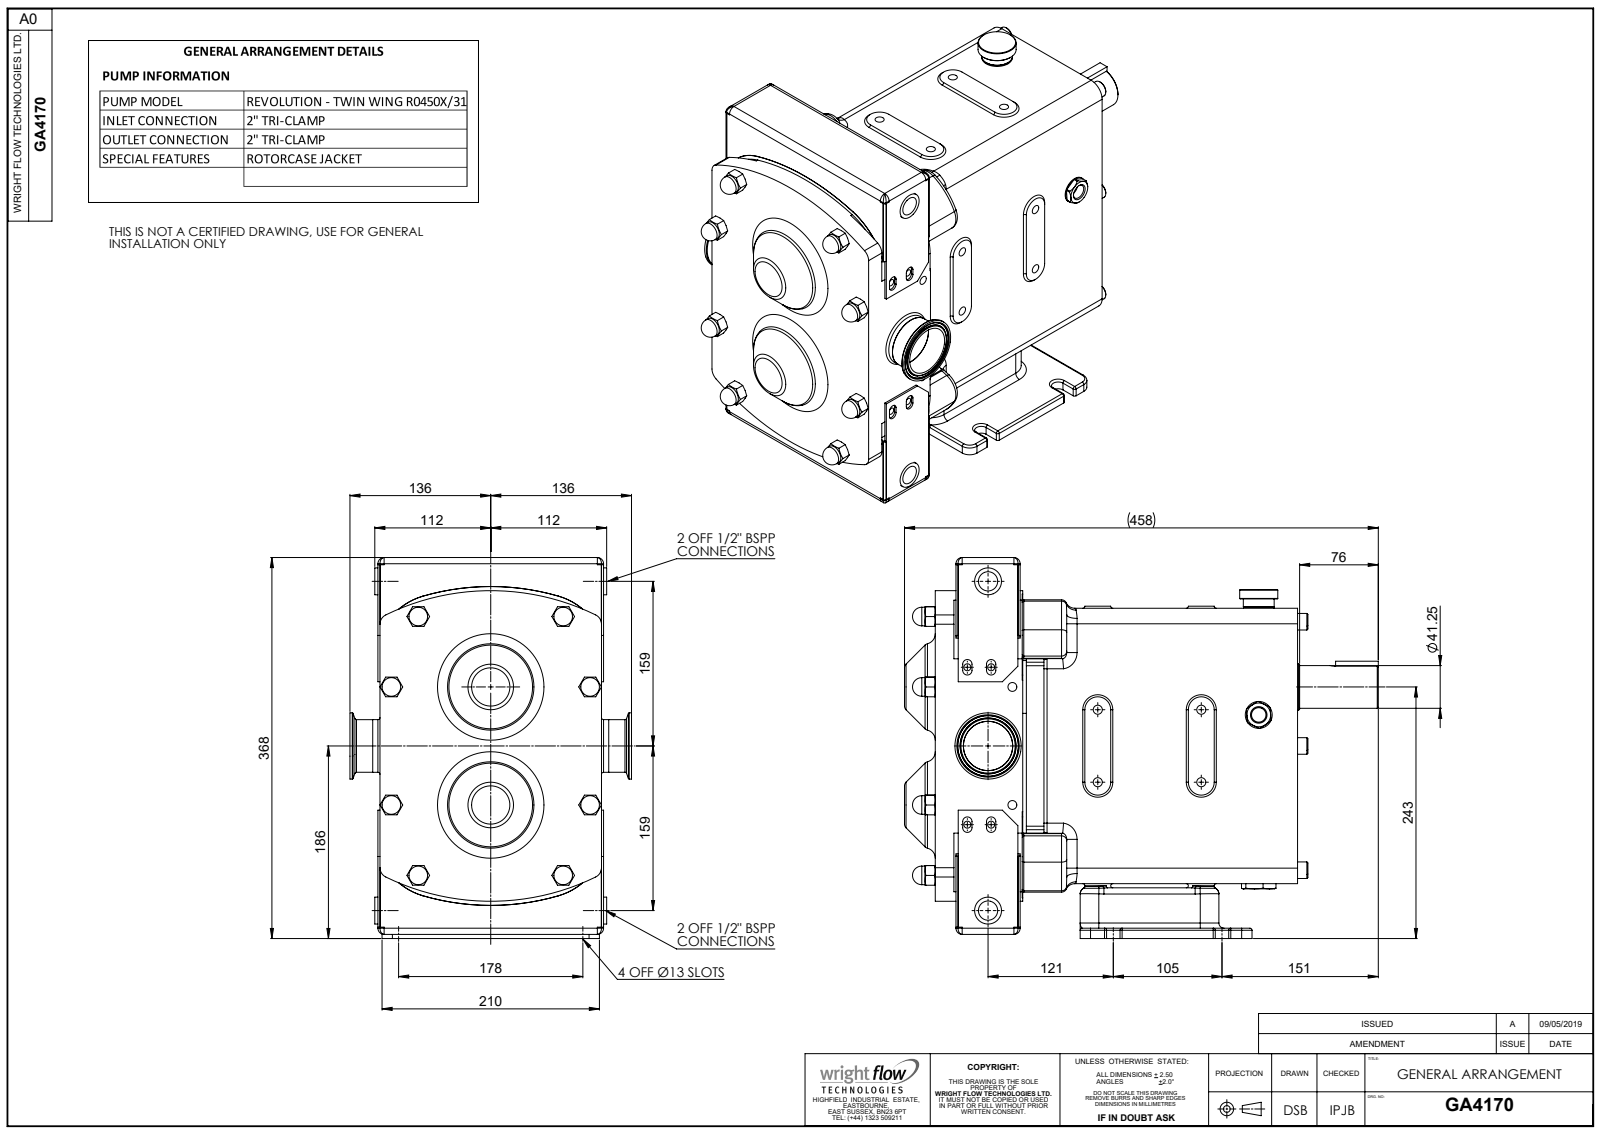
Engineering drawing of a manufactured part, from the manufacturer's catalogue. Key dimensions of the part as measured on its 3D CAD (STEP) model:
Part name (STEP PRODUCT): Copy of Size 4 Bolt on Jacket RC^GA4170; Copy of RA94-5121-33M^GA4170; Copy of R0450 CPP H TSD^GA4170; GA4170
STEP written by: SolidWorks 2023 (AUTOMOTIVE_DESIGN)
Units: millimetres
Bodies: 11 solids, 1242 faces (435 planar, 414 cylindrical, 393 other)
Overall size (bounding box): 457.7 × 368 × 272
Volume: 16 830 000 mm³ · Surface area: 929 218 mm²
Round holes (diameter × count): ⌀8.8 ×8, ⌀6.8 ×4, ⌀8.6 ×2, ⌀18.6 ×2, ⌀14 ×1, ⌀33.8 ×1, ⌀47.6 ×1, ⌀47.65 ×1
Round bosses / shafts (diameter × count): ⌀18 ×8, ⌀16 ×6, ⌀26 ×3, ⌀30 ×2, ⌀64 ×1, ⌀51 ×1, ⌀50.9 ×1, ⌀50.8 ×1
Partial cylindrical surfaces — rounded edges, fillets, slot ends (radius × count): R2 ×42, R10 ×30, R5 ×19, R6 ×12, R4 ×8, R4.5 ×8, R5.9 ×8, R15 ×8
Main face-to-face distances: 2, 31, 183, 152, 4, 6, 84.5, 265.5, 350, 43
Hole centre spacings: 70, 85.38, 100, 122.07, 23, 27.95, 47.47, 55.72
